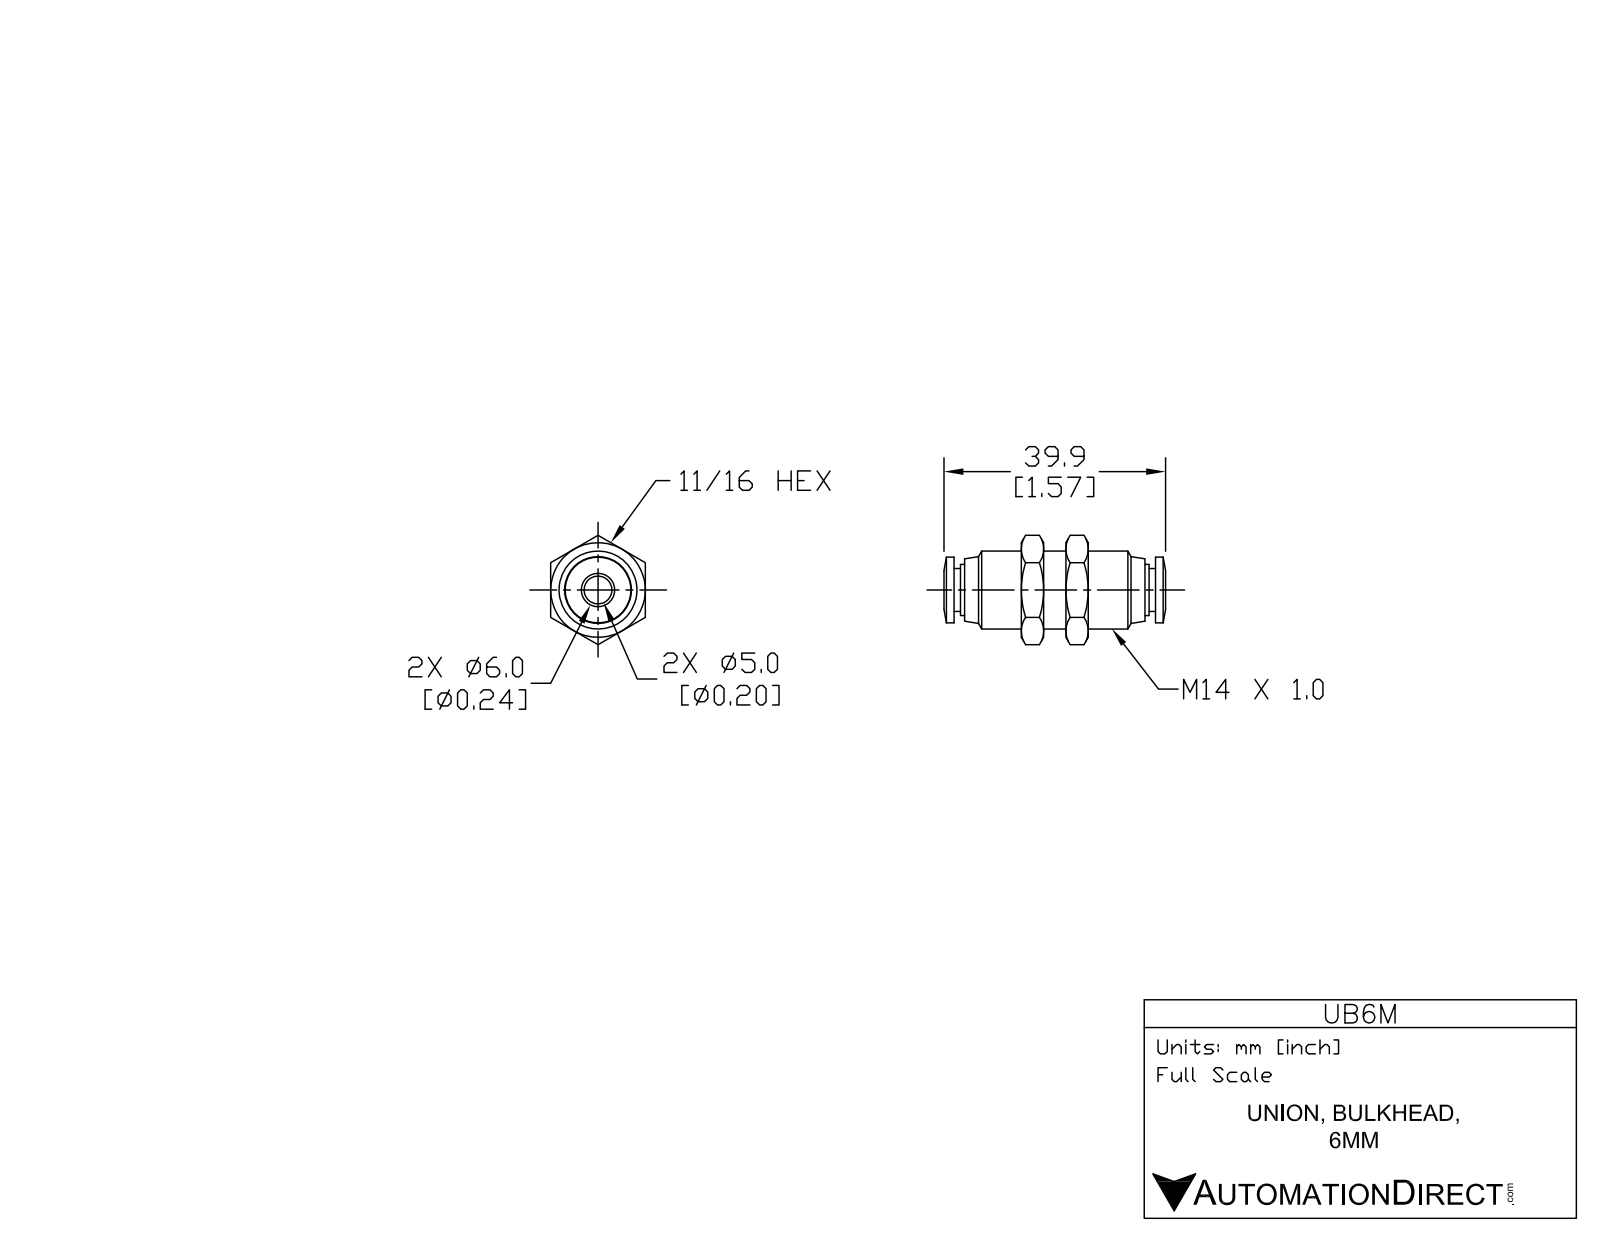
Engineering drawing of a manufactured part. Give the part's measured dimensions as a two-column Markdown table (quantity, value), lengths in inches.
| quantity | value |
| --- | --- |
| part name | UB6M |
| STEP written by | SolidWorks 2015 (AUTOMOTIVE_DESIGN) |
| units | inches |
| bodies | 1 solid, 94 faces (26 planar, 24 cylindrical, 44 other) |
| overall size | 1.567 × 0.773 × 0.669 |
| volume | 0.298 in³ |
| surface area | 5.052 in² |
| round holes (diameter × count) | 0.197 × 1, 0.248 × 1 |
| round bosses / shafts (diameter × count) | 0.551 × 1, 0.465 × 1, 0.362 × 1, 0.303 × 1 |
| main face-to-face distances | 0.157, 0.669, 0.315, 0.476, 0.634, 0.791, 0.949, 0.472, 0.075, 1.35 |
